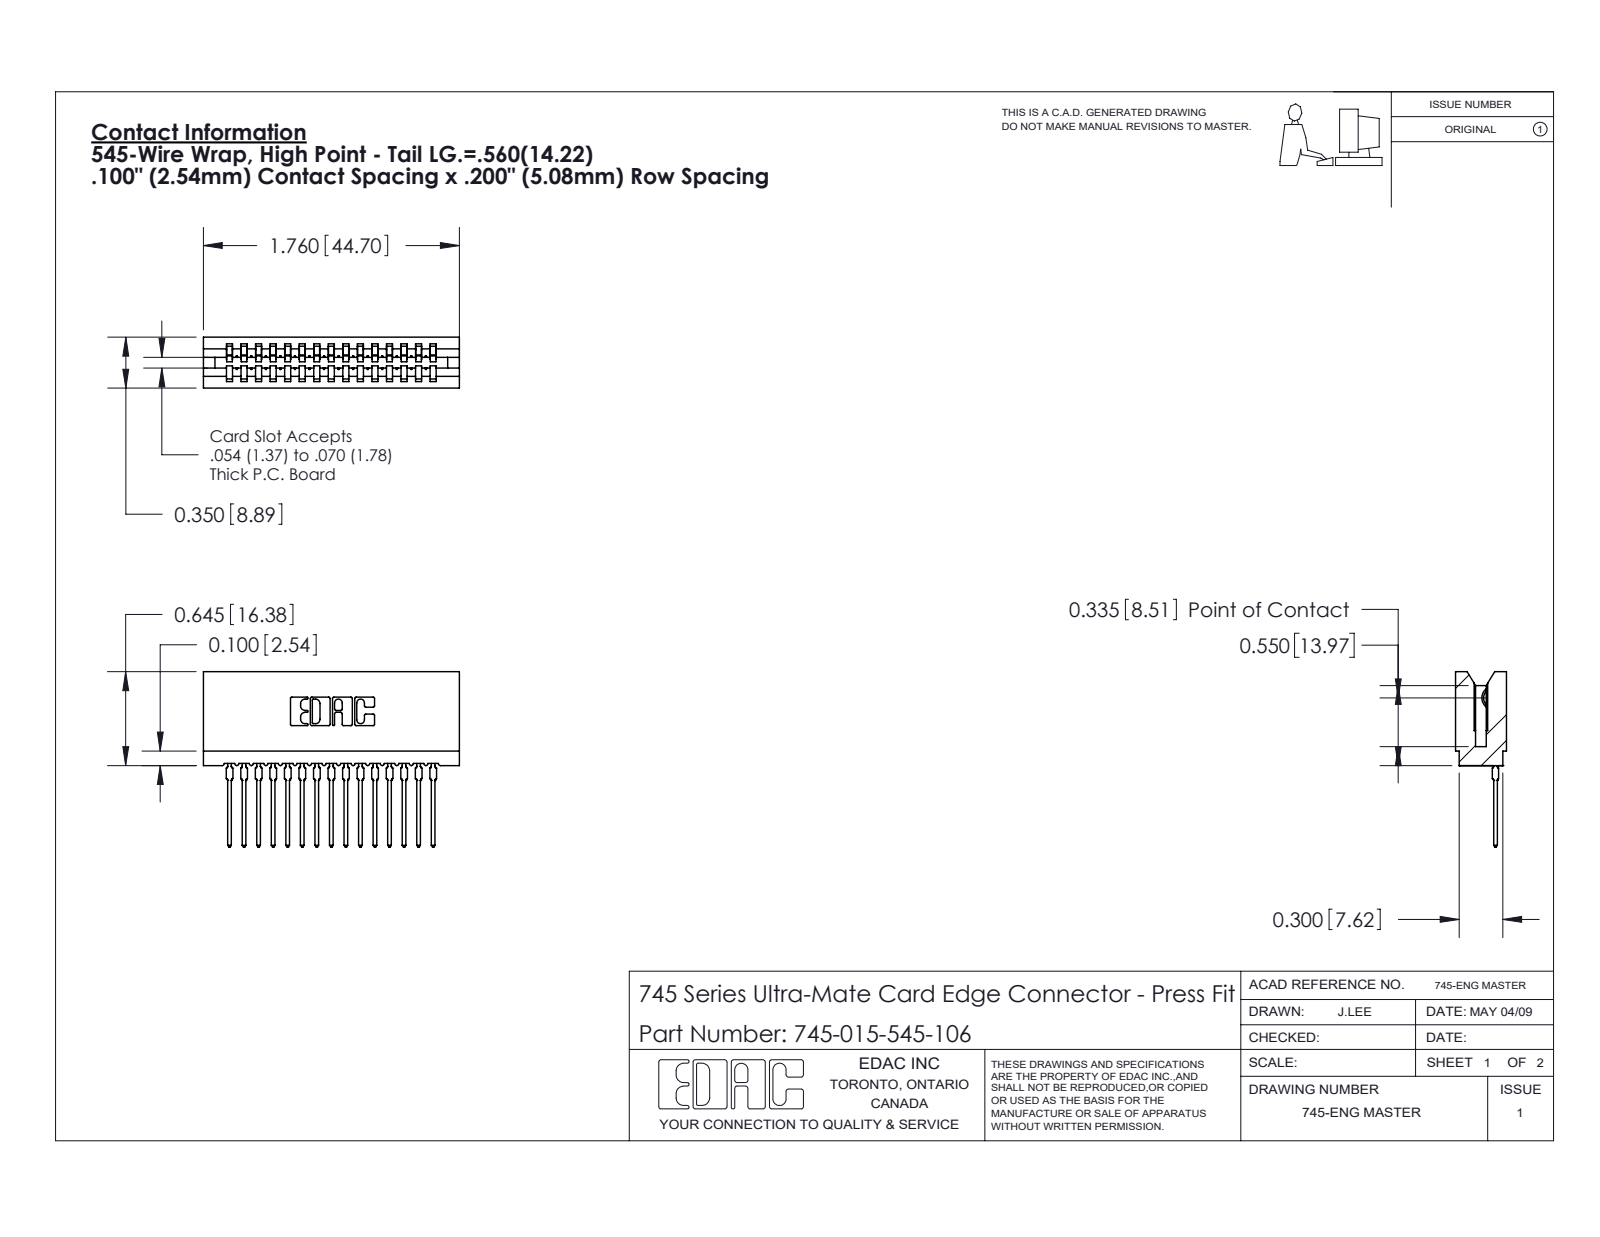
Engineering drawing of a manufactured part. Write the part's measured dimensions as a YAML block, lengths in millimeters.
part_name: "745-292-001_545; 745-015-545-106; 745 Part_Insulator Option - 06"
step_written_by: "SolidWorks 2020 (CONFIG_CONTROL_DESIGN)"
units: millimeters
bodies: {solids: 16, faces: 1776, planar: 1061, cylindrical: 325, other: 390}
overall_size: [44.7, 30.6, 8.9]
volume: 4080
surface_area: 7303
partial_cylinders:
  - {radius: 0.4, count: 30}
  - {radius: 0.5, count: 30}
  - {radius: 0.3, count: 22}
  - {radius: 0.2, count: 6}
  - {radius: 0.8, count: 6}
  - {radius: 0.1, count: 4}
  - {radius: 0.3, count: 4}
  - {radius: 0.7, count: 3}
face_to_face_distances: [2.5, 5.1, 7.6, 10.2, 8.9, 12.7, 15.2, 17.8, 3.5, 5.4]
